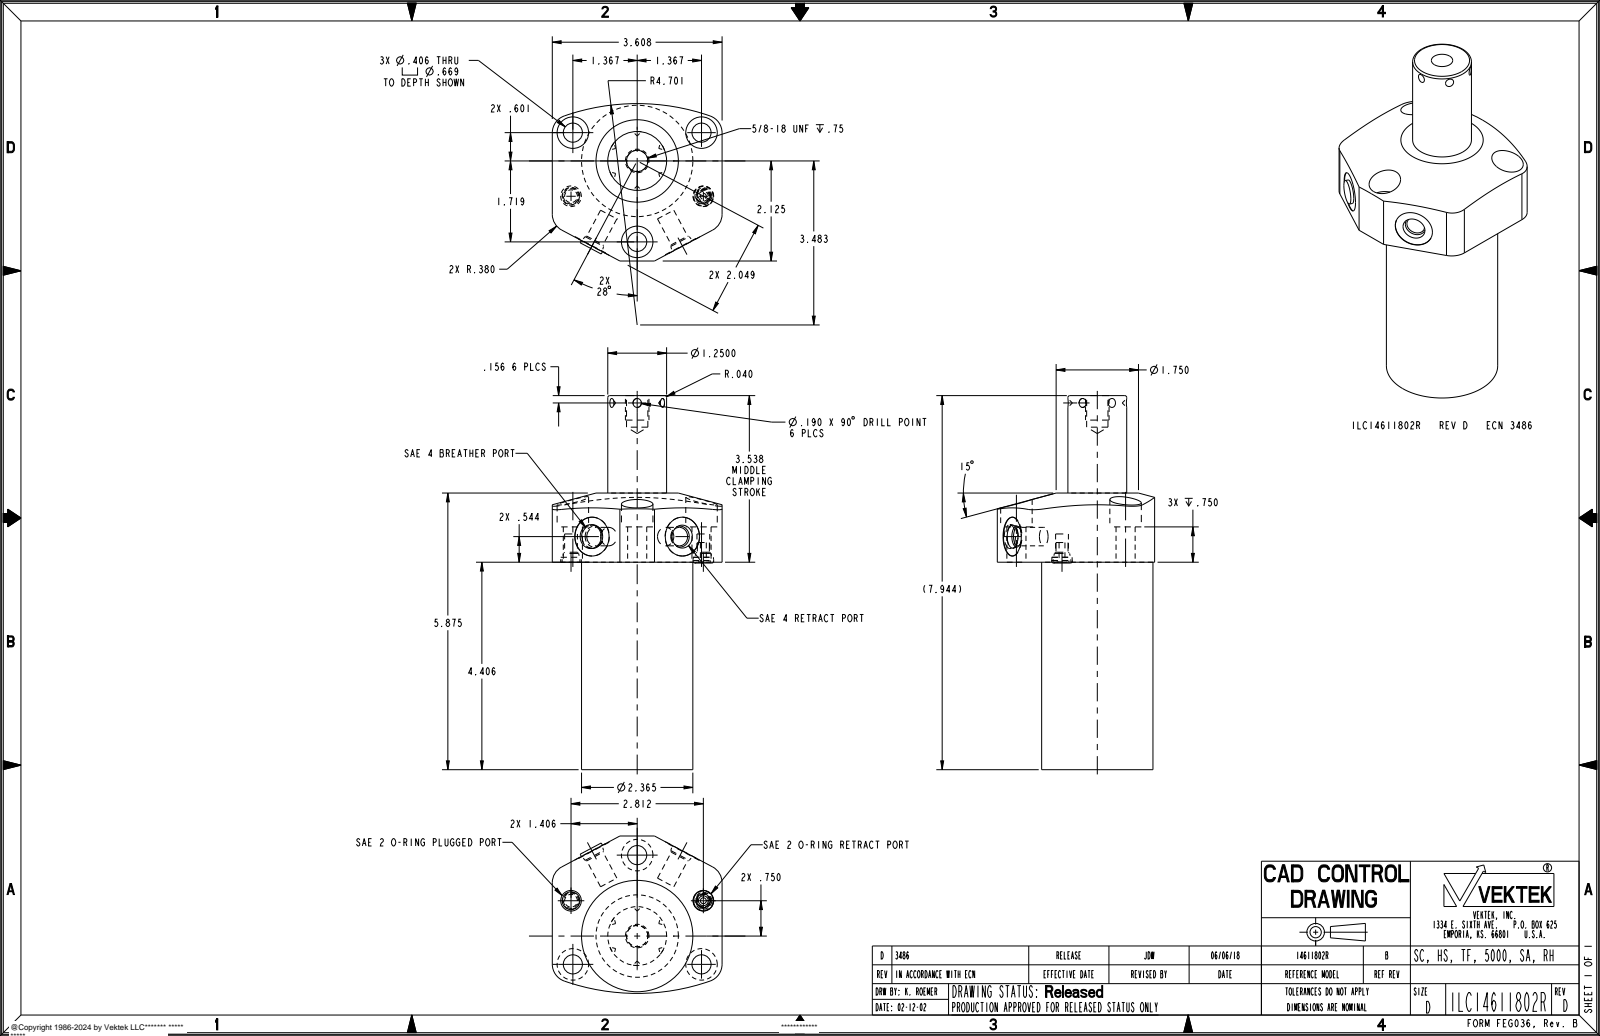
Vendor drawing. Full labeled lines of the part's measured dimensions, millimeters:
Part name (STEP PRODUCT): ILC14611802R
STEP written by: PRO/ENGINEER BY PARAMETRIC TECHNOLOGY CORPORATION, 2013320 (AUTOMOTIVE_DESIGN)
Units: millimetres
Bodies: 1 solid, 121 faces (30 planar, 53 cylindrical, 38 other)
Overall size (bounding box): 201.8 × 91.6 × 84.9
Volume: 570 300 mm³ · Surface area: 56 970 mm²
Round holes (diameter × count): ⌀10.3 ×3, ⌀17 ×3, ⌀6.9 ×2, ⌀10 ×2, ⌀11.1 ×2, ⌀21 ×2, ⌀3.2 ×1, ⌀11.5 ×1
Round bosses / shafts (diameter × count): ⌀60.1 ×1, ⌀31.8 ×1, ⌀12.9 ×1, ⌀12.7 ×1, ⌀10.9 ×1, ⌀9.6 ×1, ⌀6.5 ×1, ⌀5.3 ×1
Partial cylindrical surfaces — rounded edges, fillets, slot ends (radius × count): R9.7 ×4, R119.4 ×1
Main face-to-face distances: 111.9, 91.6, 149.2, 37.3, 201.8, 89.9, 52.6, 19.1, 131, 18.3
Hole centre spacings: 34.3, 37.9, 40.5, 43.4, 68.4, 78.4, 43.7, 69.4
